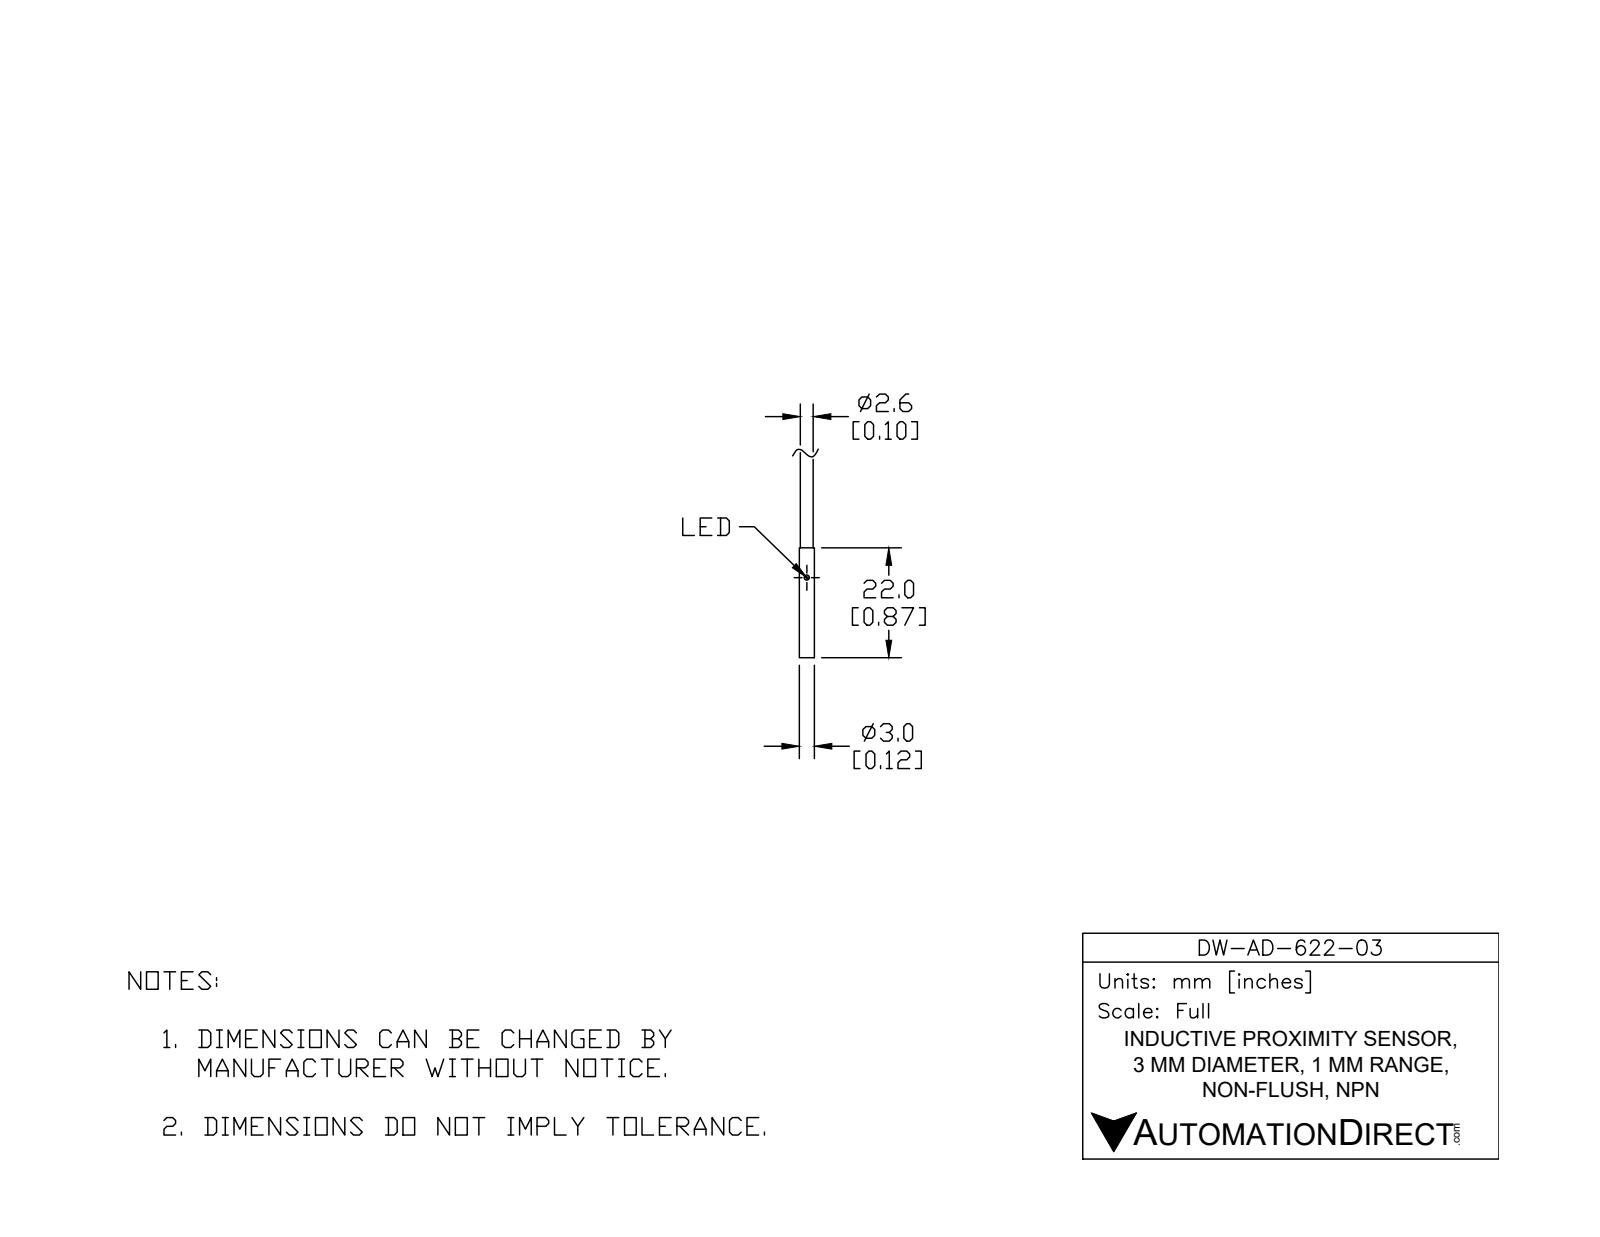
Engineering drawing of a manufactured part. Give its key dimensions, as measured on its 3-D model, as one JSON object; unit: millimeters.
{"part_name": "DW-AD-622-03", "step_written_by": "SolidWorks 2017 (AUTOMOTIVE_DESIGN)", "units": "millimeters", "bodies": {"solids": 3, "faces": 13, "planar": 5, "cylindrical": 5, "other": 3}, "overall_size": [36, 3, 3], "volume_mm3": 100, "surface_area_mm2": 577, "round_holes": [[1, 1], [2.7, 1]], "round_bosses_or_shafts": [[3, 1], [2.6, 1]], "face_to_face_distances": [0.8, 17, 16.2, 22, 21.2, 5]}
